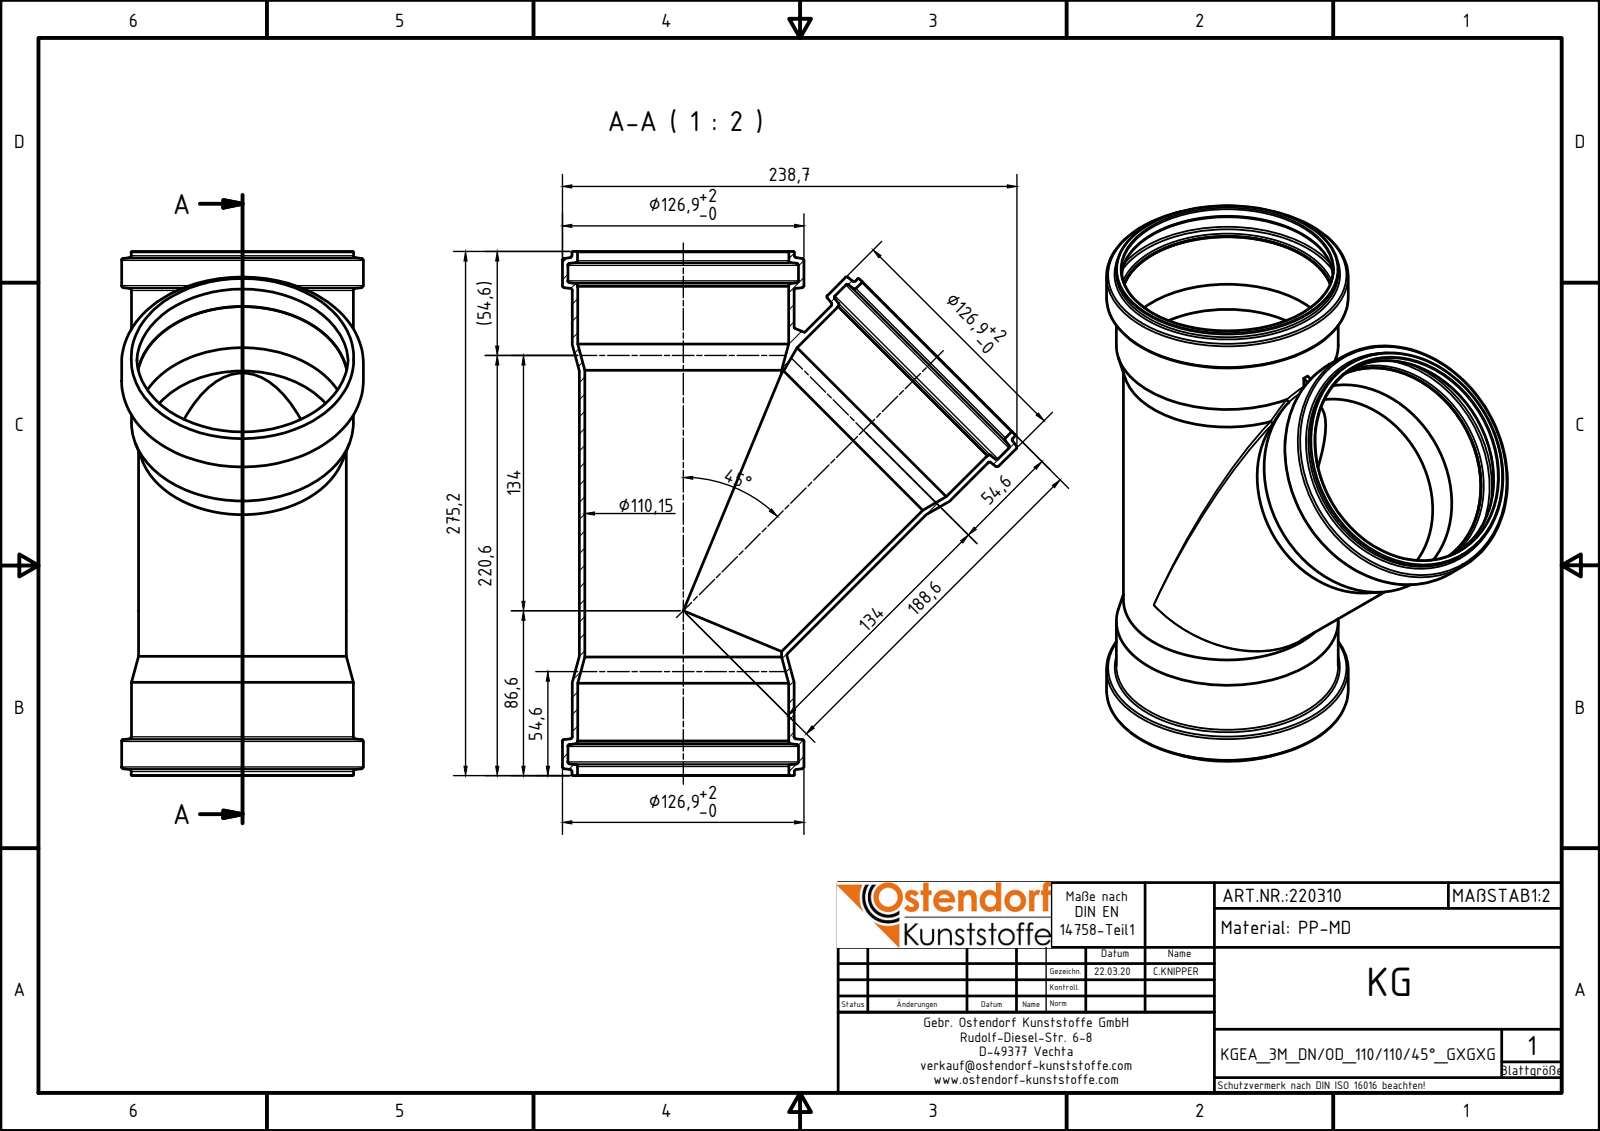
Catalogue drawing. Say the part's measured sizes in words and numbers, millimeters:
The part is named "Abzweiger KG DN100x100x45 GxGxG". Its 3-D file was written by "Autodesk Inventor 2020 (AUTOMOTIVE_DESIGN)". It is 1 solid with 89 faces: 9 planar, 25 cylindrical and 55 other. Overall it measures 275.2 by 238.69 by 126.9 millimeters. Its volume is 422 013 cubic millimeters and its surface area 276 829 square millimeters. Round holes: 2 of diameter 103.75, 2 of diameter 110.7, 2 of diameter 111, 2 of diameter 121.1. Round bosses or shafts: 2 of diameter 126.9, 2 of diameter 116.8, 2 of diameter 116.5, 2 of diameter 110.15. The main face-to-face distances are 275.2, 18.22, 256.98, 238.76, 3.
